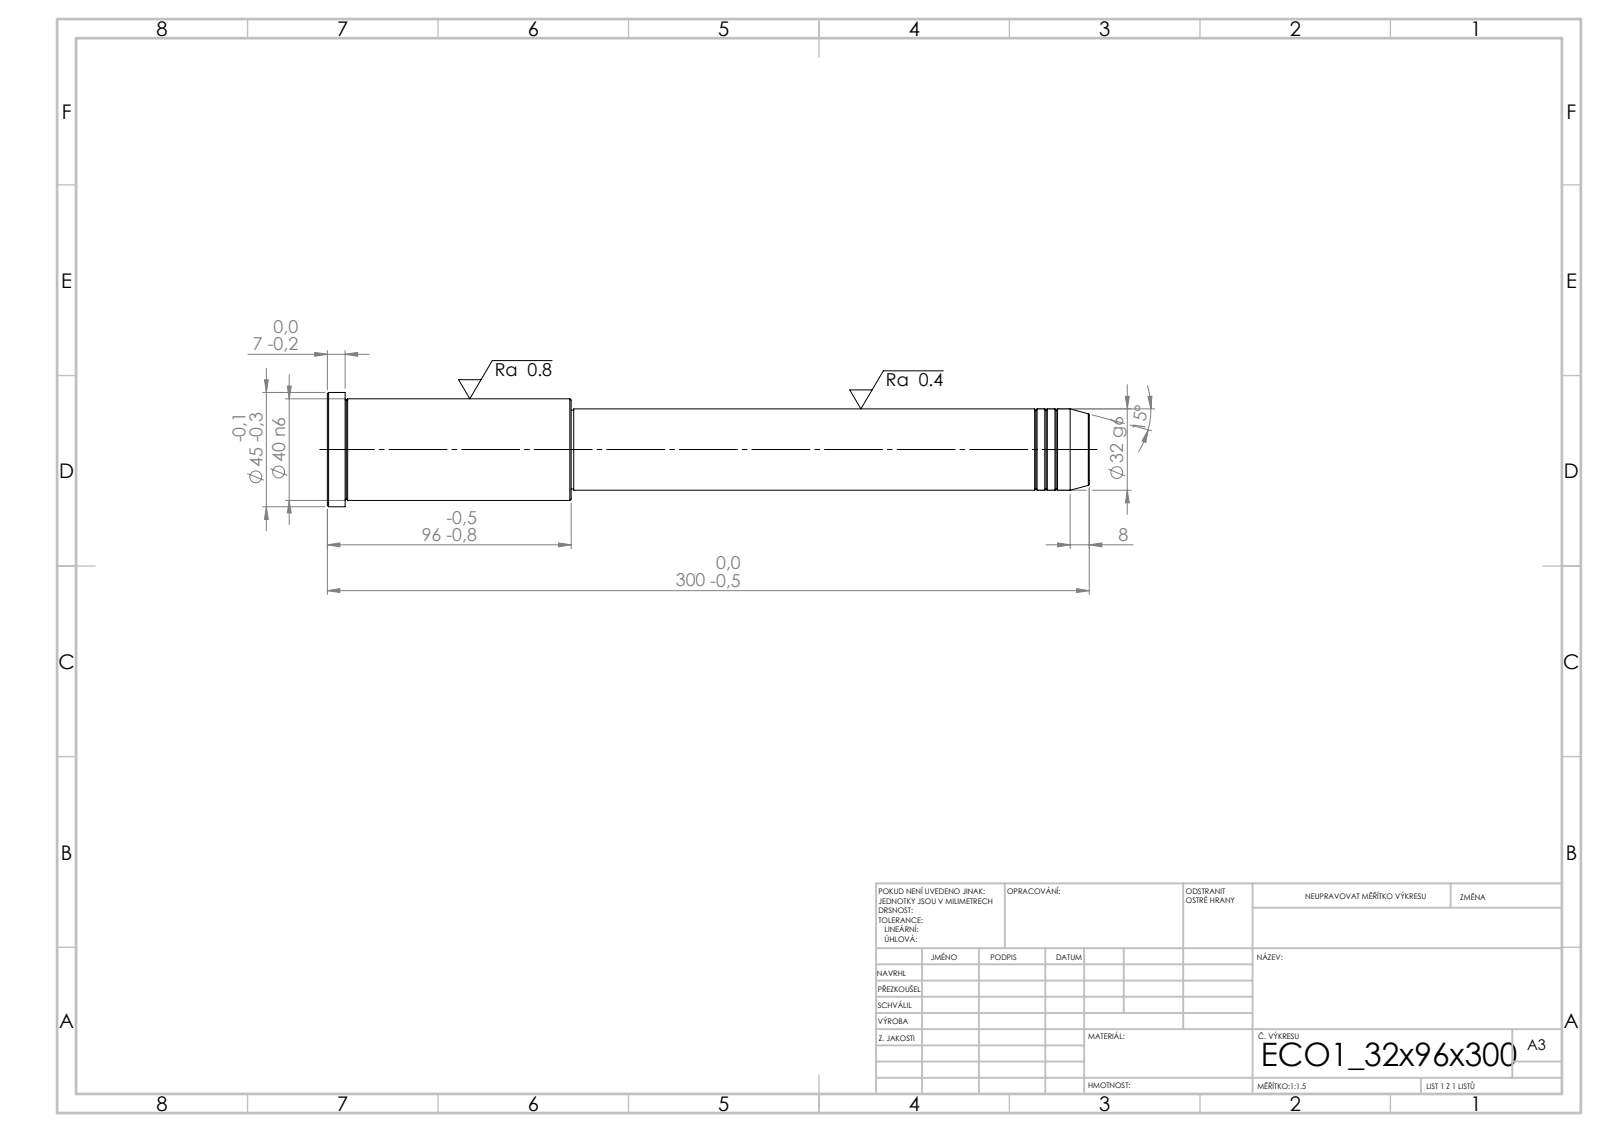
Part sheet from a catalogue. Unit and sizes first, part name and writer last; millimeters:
Units: millimetres
Overall size (bounding box): 300 × 45 × 45
Round bosses / shafts (diameter × count): ⌀45 ×1, ⌀40 ×1, ⌀32 ×1, ⌀31 ×1
Main face-to-face distances: 300, 204, 96, 293, 89, 7, 203, 1, 90, 97
Volume: 286 064 mm³ · Surface area: 35 889 mm²
Bodies: 1 solid, 43 faces (5 planar, 14 cylindrical, 24 other)
STEP written by: SolidWorks 2019 (CONFIG_CONTROL_DESIGN)
